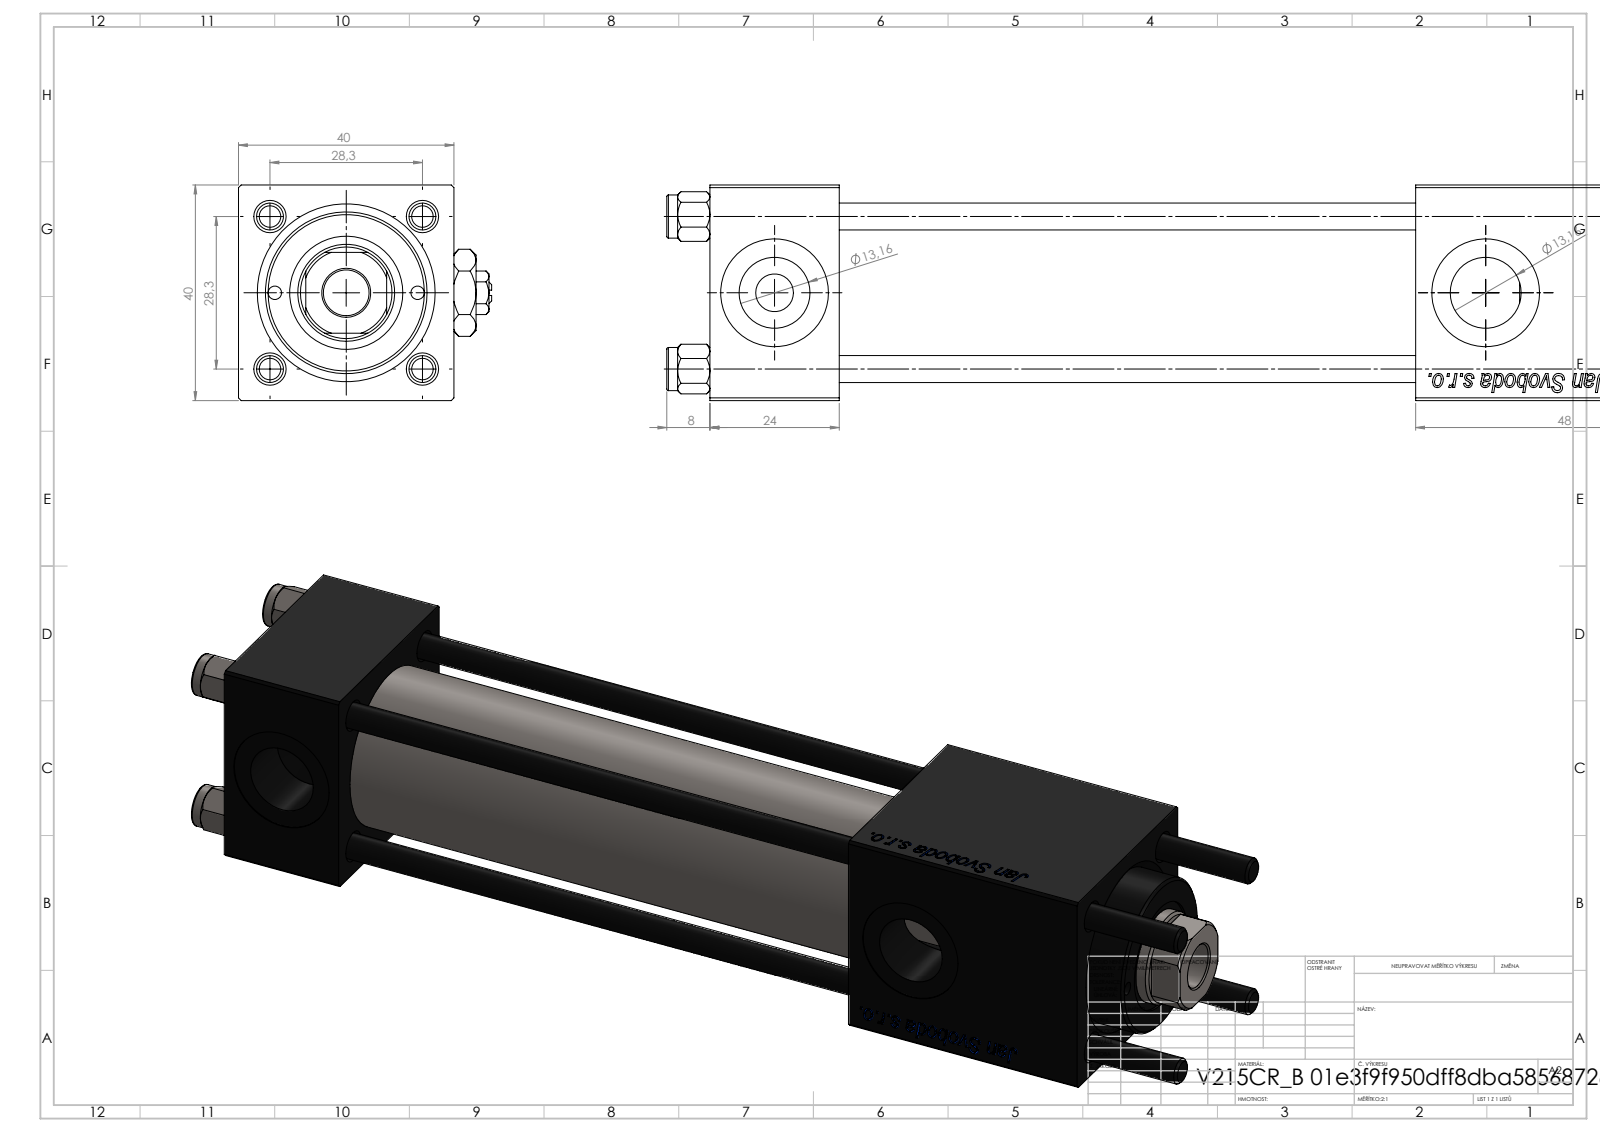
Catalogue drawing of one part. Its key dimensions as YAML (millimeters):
part_name: "V215CR_B-1; V215CR_VCP_B; V215_VC_A; Zatka_pro_OIL_PORT (+2 more)"
step_written_by: "SolidWorks 2019 (CONFIG_CONTROL_DESIGN)"
units: millimeters
bodies: {solids: 13, faces: 1259, planar: 477, cylindrical: 92, other: 690}
overall_size: [206, 47, 40]
volume: 186784
surface_area: 80569
round_holes:
  - {diameter: 5, count: 4}
  - {diameter: 20, count: 3}
  - {diameter: 2.5, count: 2}
  - {diameter: 7, count: 2}
  - {diameter: 13.16, count: 2}
  - {diameter: 8.5, count: 1}
  - {diameter: 18, count: 1}
  - {diameter: 21, count: 1}
  - {diameter: 25, count: 1}
  - {diameter: 30, count: 1}
round_bosses_or_shafts:
  - {diameter: 8, count: 4}
  - {diameter: 31, count: 1}
partial_cylinders:
  - {radius: 8.5, count: 1}
face_to_face_distances: [40, 24, 39.8, 131, 107, 150.3, 126.3, 19.3, 179, 155]
hole_center_spacings: [14.18, 20.01, 28.3, 30.84, 13.25, 40.02, 26.5, 132]
